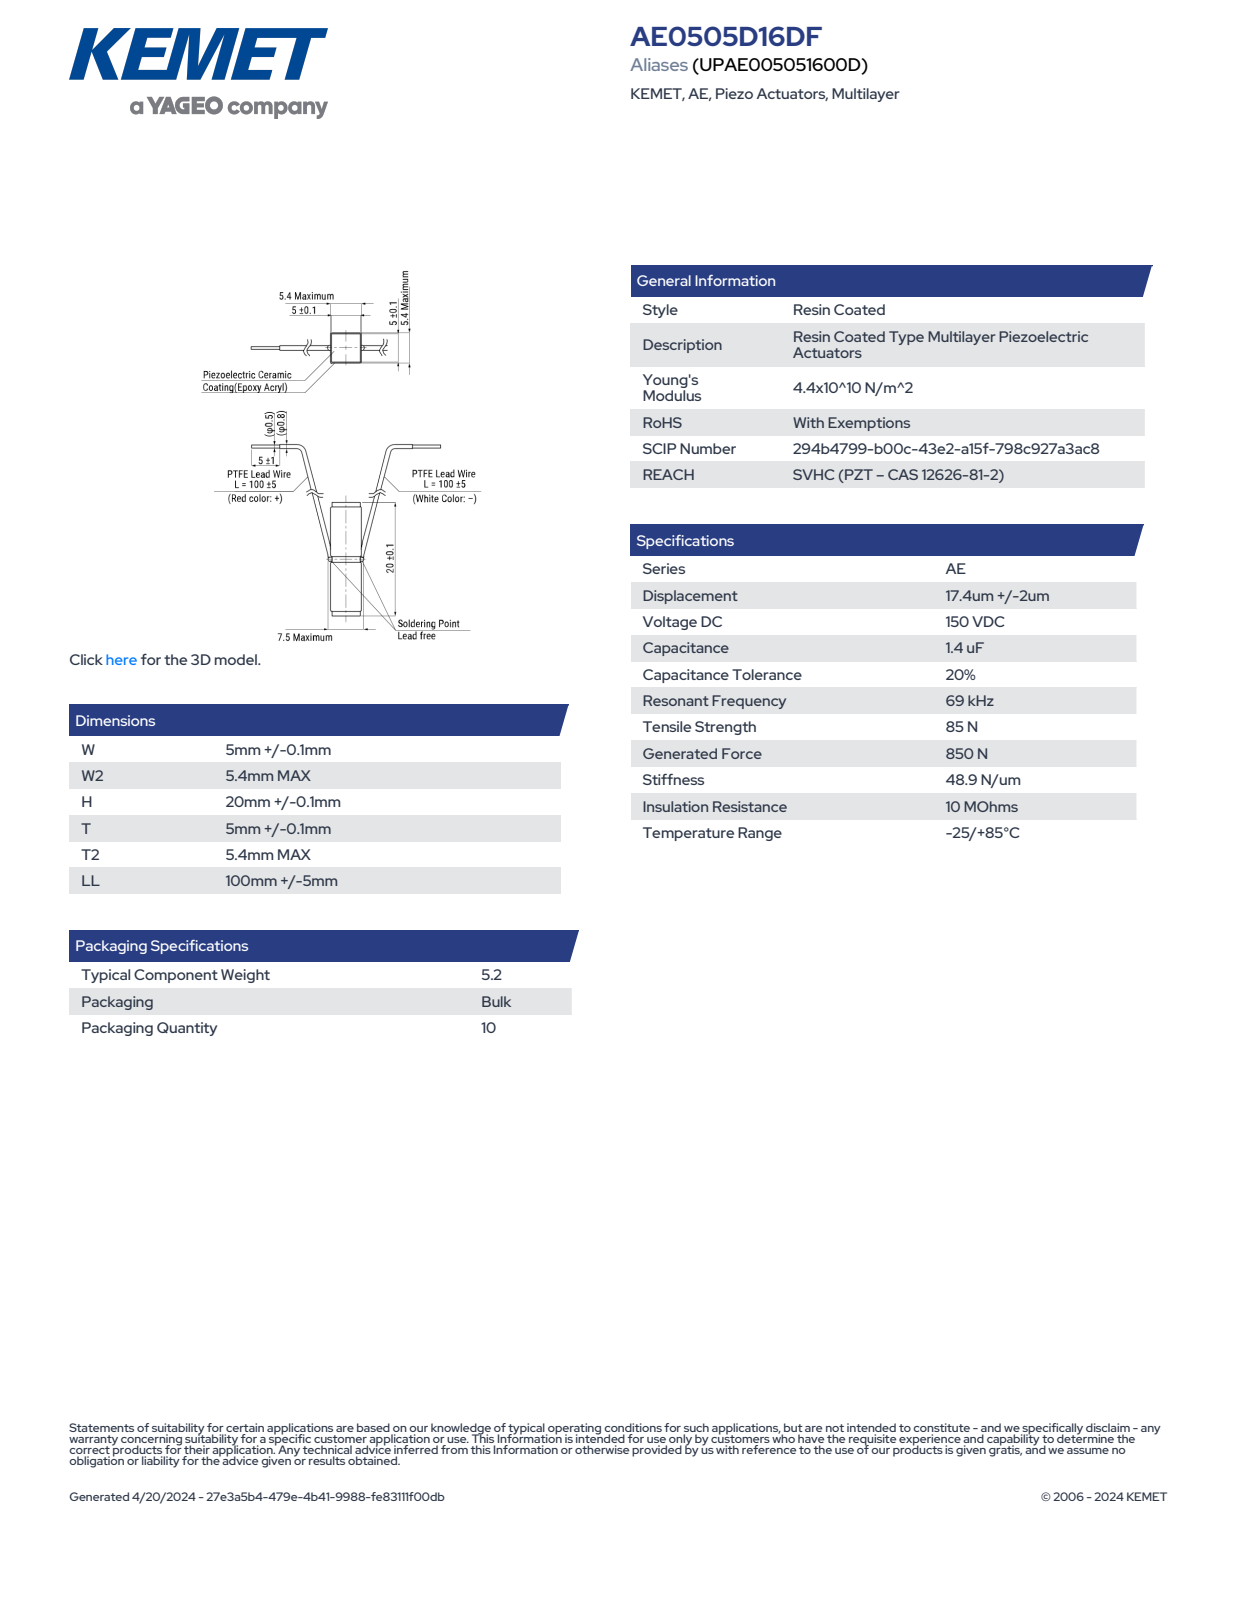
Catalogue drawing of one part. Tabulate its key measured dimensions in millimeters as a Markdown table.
| quantity | value |
| --- | --- |
| part name | AL_KAE1_W5.1W25.4H20.1T5.1T25.4 |
| STEP written by | SolidWorks 2014 (AUTOMOTIVE_DESIGN) |
| units | millimeters |
| bodies | 4 solids, 93 faces (85 planar, 8 cylindrical, 0 other) |
| overall size | 20.11 × 5.4 × 5.4 |
| volume | 523 mm³ |
| surface area | 479 mm² |
| partial cylindrical surfaces (radius × count) | 0.15 × 8 |
| main face-to-face distances | 5.1, 5, 5.25, 4.9, 5.4, 20.1, 8.08, 12.02, 1.97, 18.13 |
